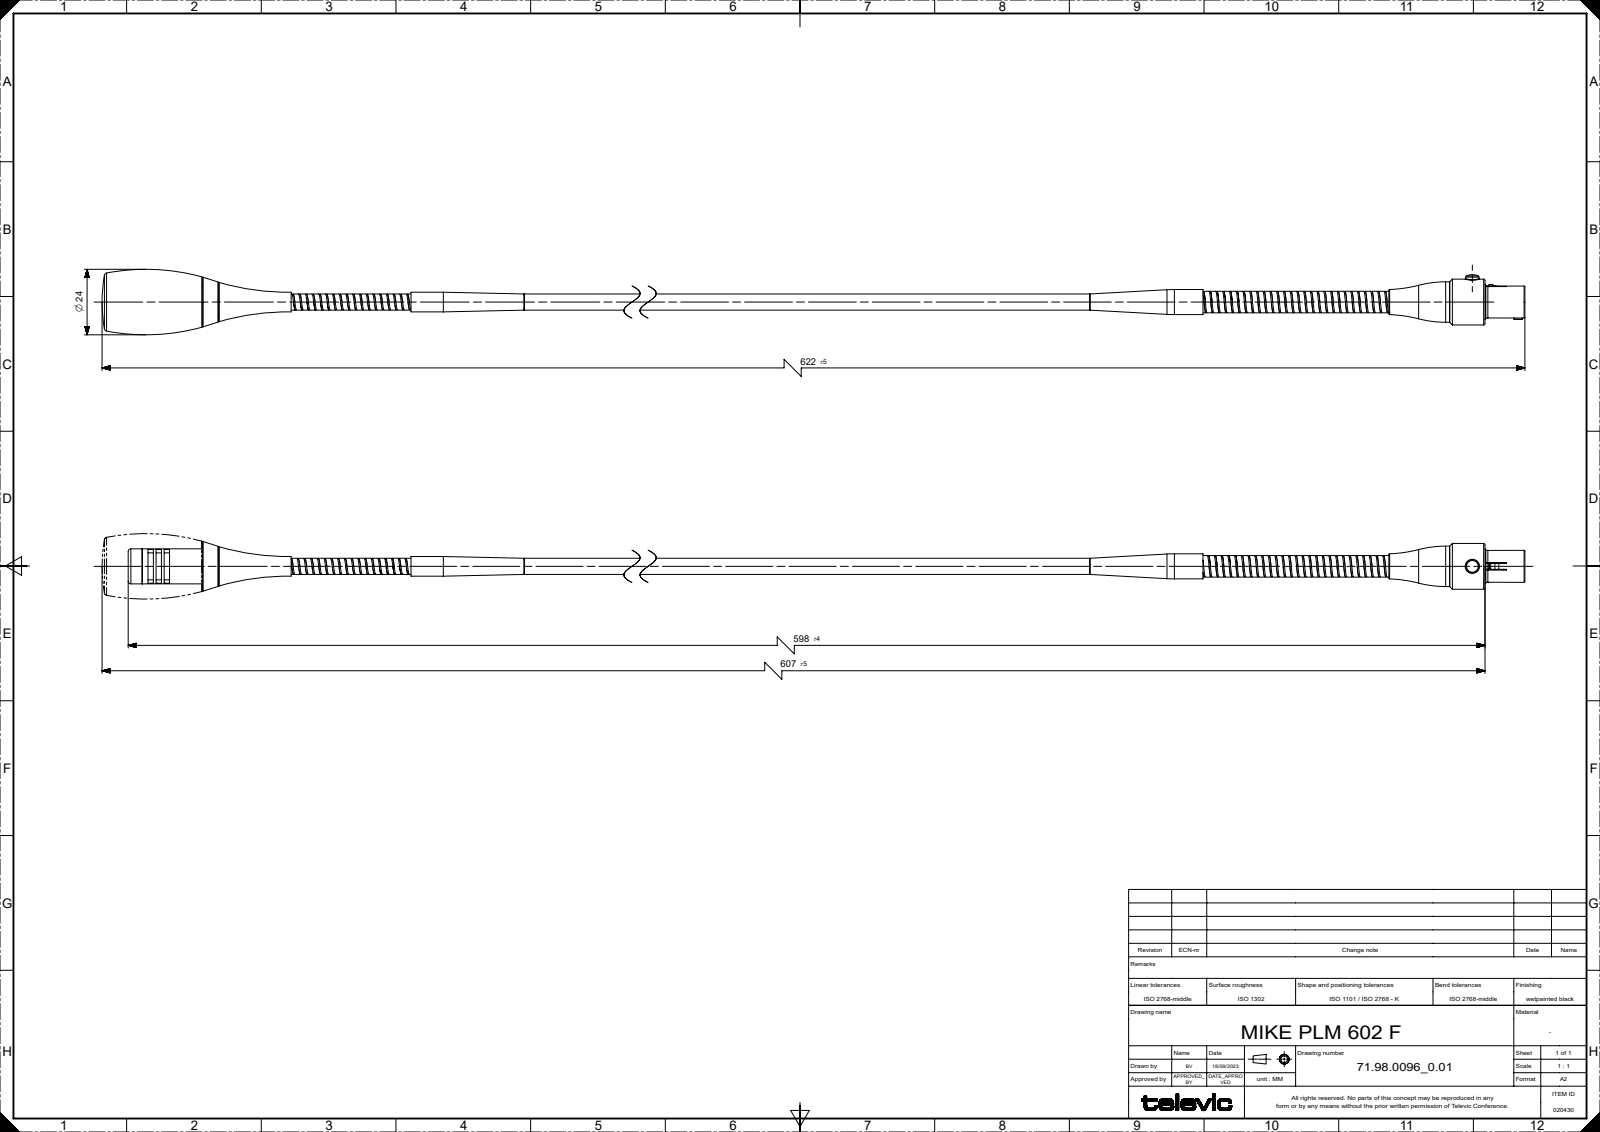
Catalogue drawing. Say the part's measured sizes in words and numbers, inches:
The part is named "004537_0.01-004537; 004539_0.01-004539; 004318_0.01-13.99.0501; 004323_0.01-004323 (+8 more)". Its 3-D file was written by "SIEMENS PLM Software NX 2000 (AUTOMOTIVE_DESIGN)". It is 14 solids with 1767 faces: 1019 planar, 590 cylindrical and 158 other. Overall it measures 24.497 by 0.957 by 0.957 inches. Its volume is 1.945 cubic inches and its surface area 57.72 square inches. Round holes: 2 of diameter 0.157, 1 of diameter 0.059, 1 of diameter 0.079, 1 of diameter 0.083, 1 of diameter 0.087, 1 of diameter 0.118, 1 of diameter 0.15, 1 of diameter 0.165, 1 of diameter 0.176, 1 of diameter 0.197, 1 of diameter 0.199, 1 of diameter 0.236. Round bosses or shafts: 1 of diameter 0.669, 1 of diameter 0.591, 1 of diameter 0.512, 1 of diameter 0.445, 1 of diameter 0.429, 1 of diameter 0.425, 1 of diameter 0.424, 1 of diameter 0.385. Partial cylindrical surfaces (rounded edges, fillets, slot ends): 86 of radius 0.004, 46 of radius 0.009, 25 of radius 0.006, 11 of radius 0.01, 8 of radius 0.005, 8 of radius 0.008, 6 of radius 0.018, 5 of radius 0.014. The main face-to-face distances are 0.039, 0.236, 22.521, 1.339, 1.102, 0.085, 22.422, 1.28, 1.044, 0.059.
